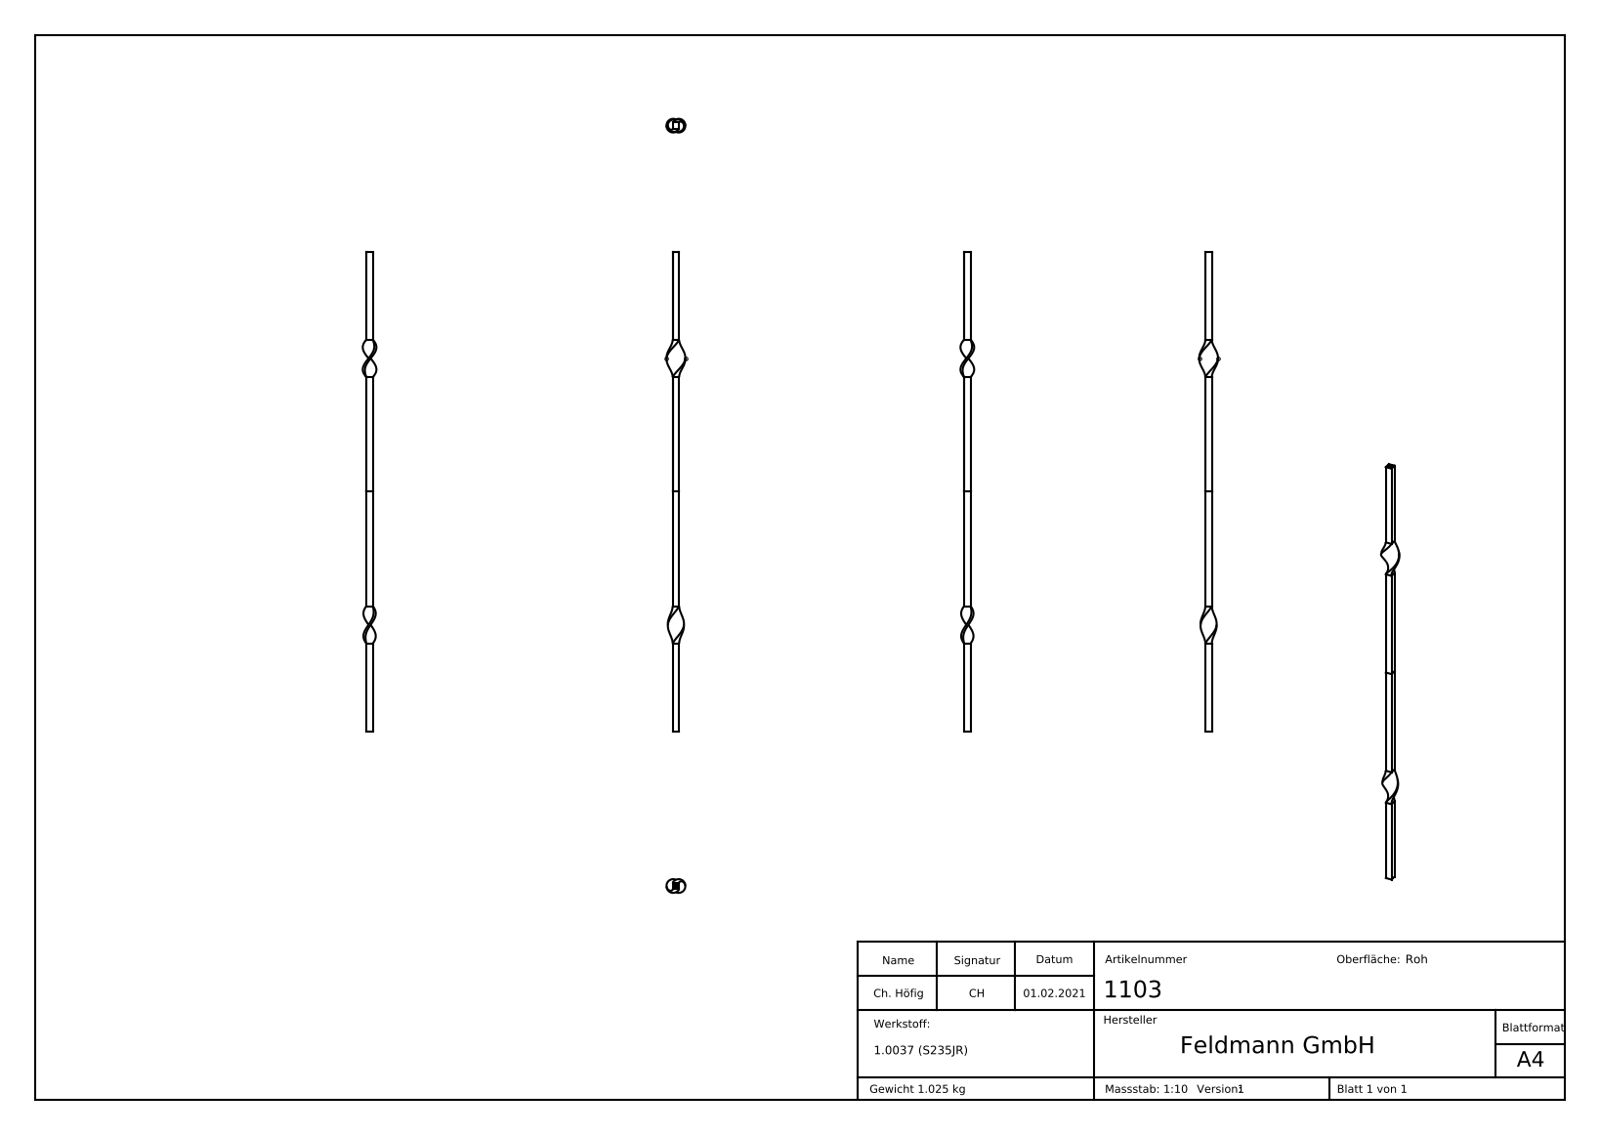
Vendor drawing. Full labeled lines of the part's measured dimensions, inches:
Part name (STEP PRODUCT): 1103
STEP written by: SolidWorks 2018 (CONFIG_CONTROL_DESIGN)
Units: inches
Bodies: 1 solid, 223 faces (124 planar, 0 cylindrical, 99 other)
Overall size (bounding box): 35.433 × 1.417 × 1.01
Volume: 8.016 in³ · Surface area: 72.02 in²
Main face-to-face distances: 0.472, 35.433, 35.429, 0.027, 0.276, 0.197, 0.013, 0.088, 0.106, 0.061
